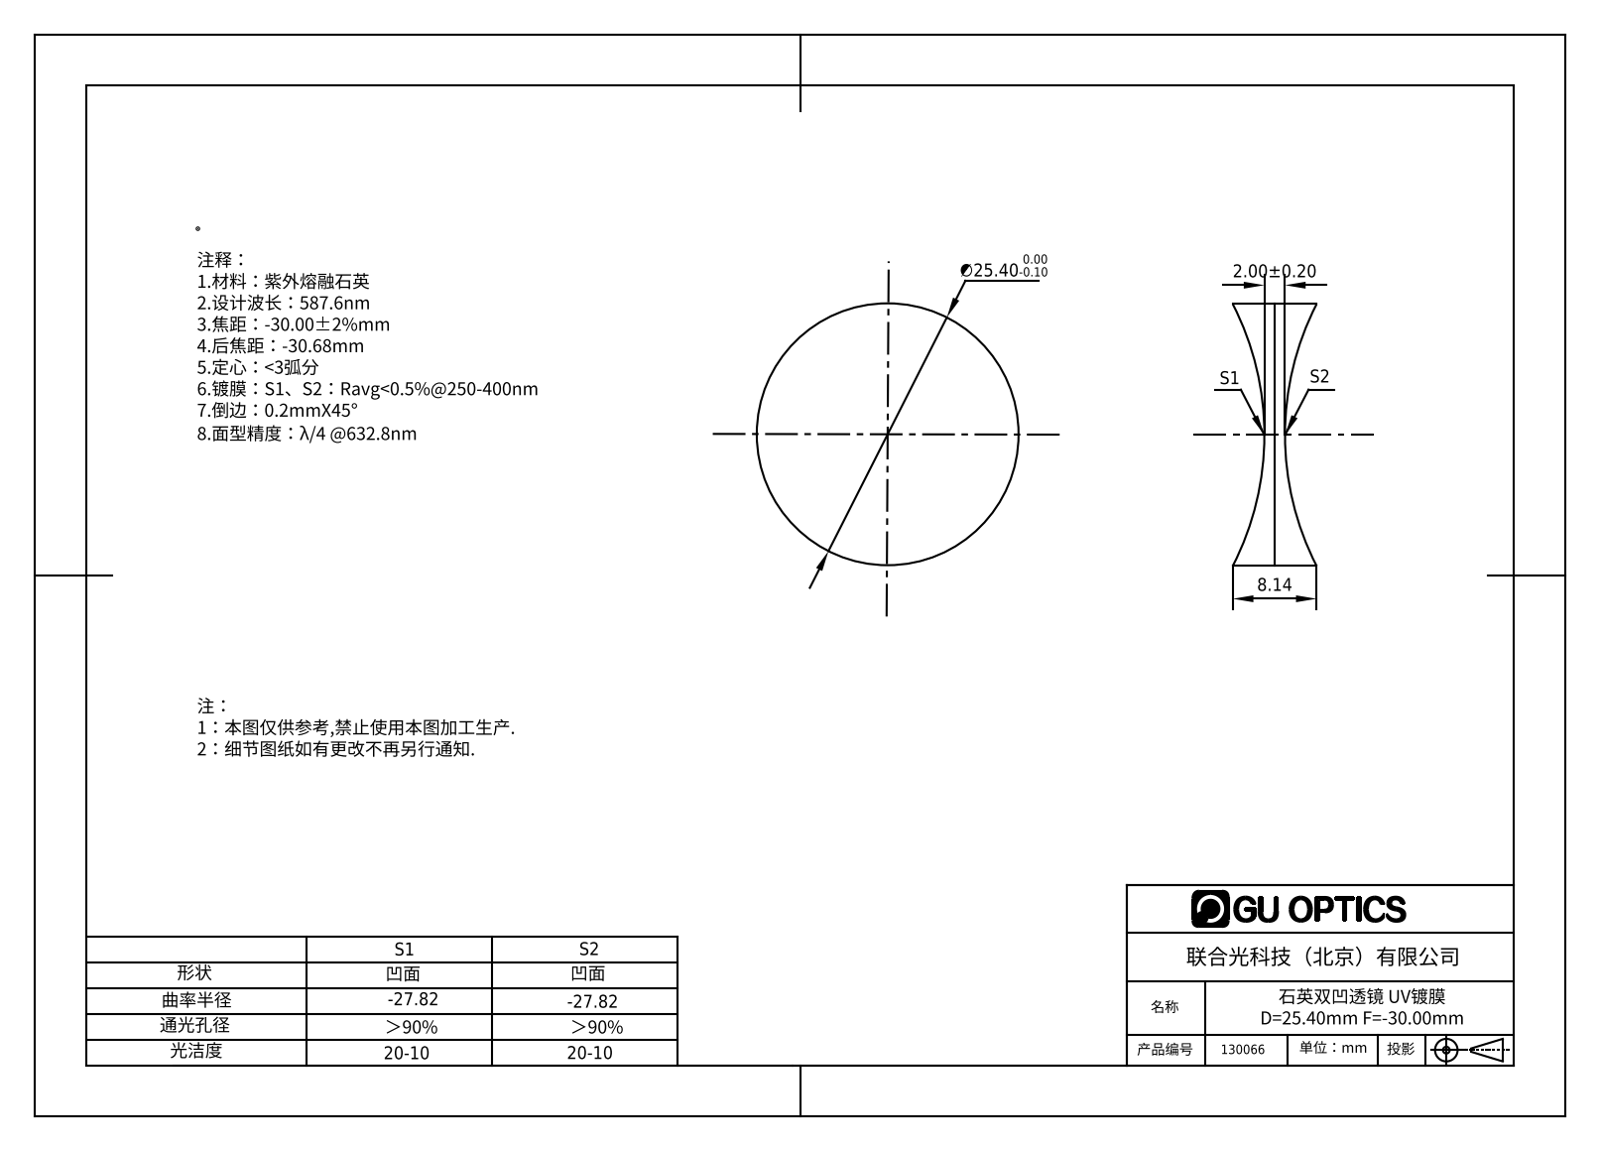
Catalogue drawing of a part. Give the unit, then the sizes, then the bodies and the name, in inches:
Units: inches
Overall size (bounding box): 1 × 1 × 0.32
Round bosses / shafts (diameter × count): ⌀1 ×1
Volume: 0.155 in³ · Surface area: 2.669 in²
Bodies: 1 solid, 6 faces (0 planar, 2 cylindrical, 4 other)
Part name (STEP PRODUCT): 150057
STEP written by: SolidWorks 2016 (AUTOMOTIVE_DESIGN)
